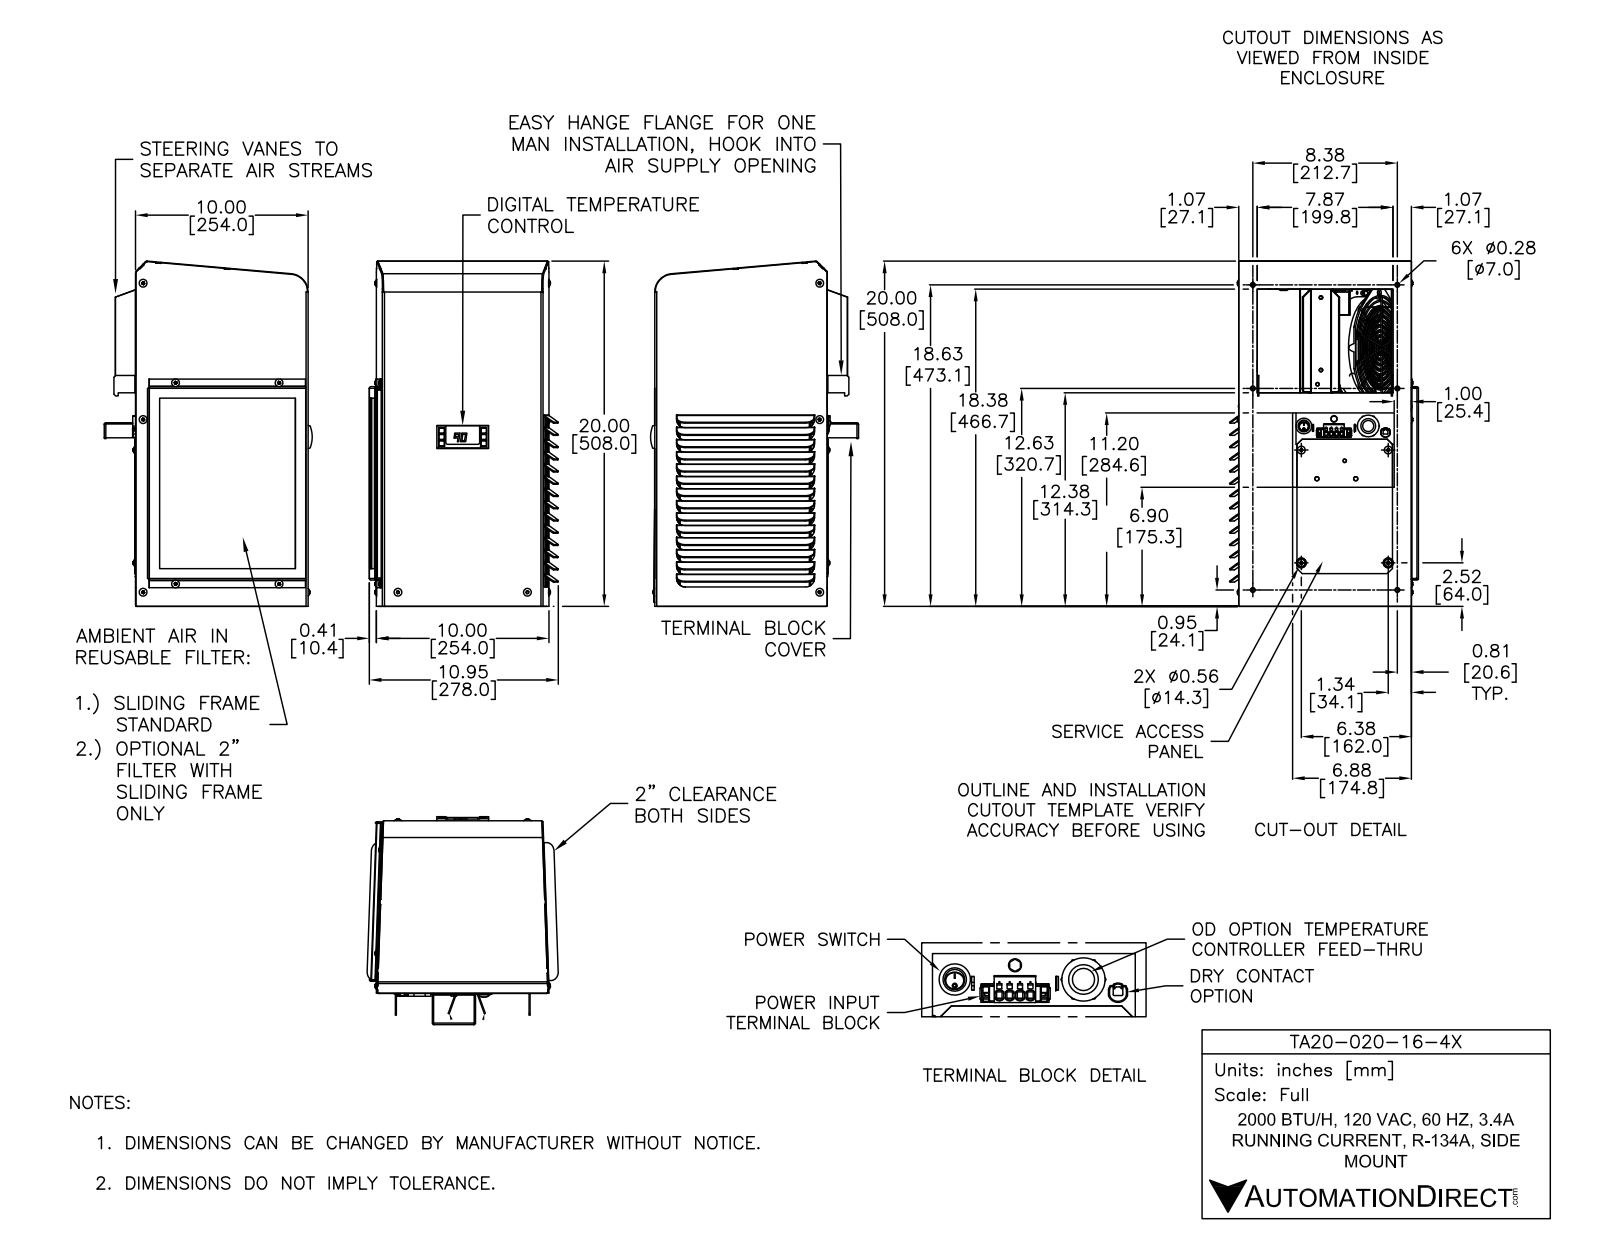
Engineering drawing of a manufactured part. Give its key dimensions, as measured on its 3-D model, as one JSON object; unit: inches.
{"part_name": "TA20-020-16-4X", "step_written_by": "SolidWorks 2019 (AUTOMOTIVE_DESIGN)", "units": "inches", "bodies": {"solids": 52, "faces": 2157, "planar": 1121, "cylindrical": 737, "other": 299}, "overall_size": [20, 11.344, 11.002], "volume_in3": 401.3, "surface_area_in2": 2755, "round_holes": [[0.204, 17], [0.2, 6], [0.344, 6], [0.045, 4], [0.12, 4], [0.14, 4], [0.166, 4], [0.219, 4], [0.091, 2], [0.126, 2], [0.166, 2], [0.25, 2]], "round_bosses_or_shafts": [[0.19, 16], [0.44, 6], [0.36, 2], [0.106, 2], [1, 1], [0.906, 1], [0.865, 1], [0.832, 1]], "partial_cylinders_radius": [[0.015, 100], [0.01, 96], [0.031, 44], [0.03, 33], [0.1, 22], [0.011, 16], [0.091, 14], [0.089, 13]], "face_to_face_distances": [0.06, 0.058, 10, 9.94, 9.942, 9.882, 0.185, 0.244, 2.624, 2.809], "hole_center_spacings": [0.2, 0.4, 6, 6, 11.65, 13.104, 8.251, 8.375]}
